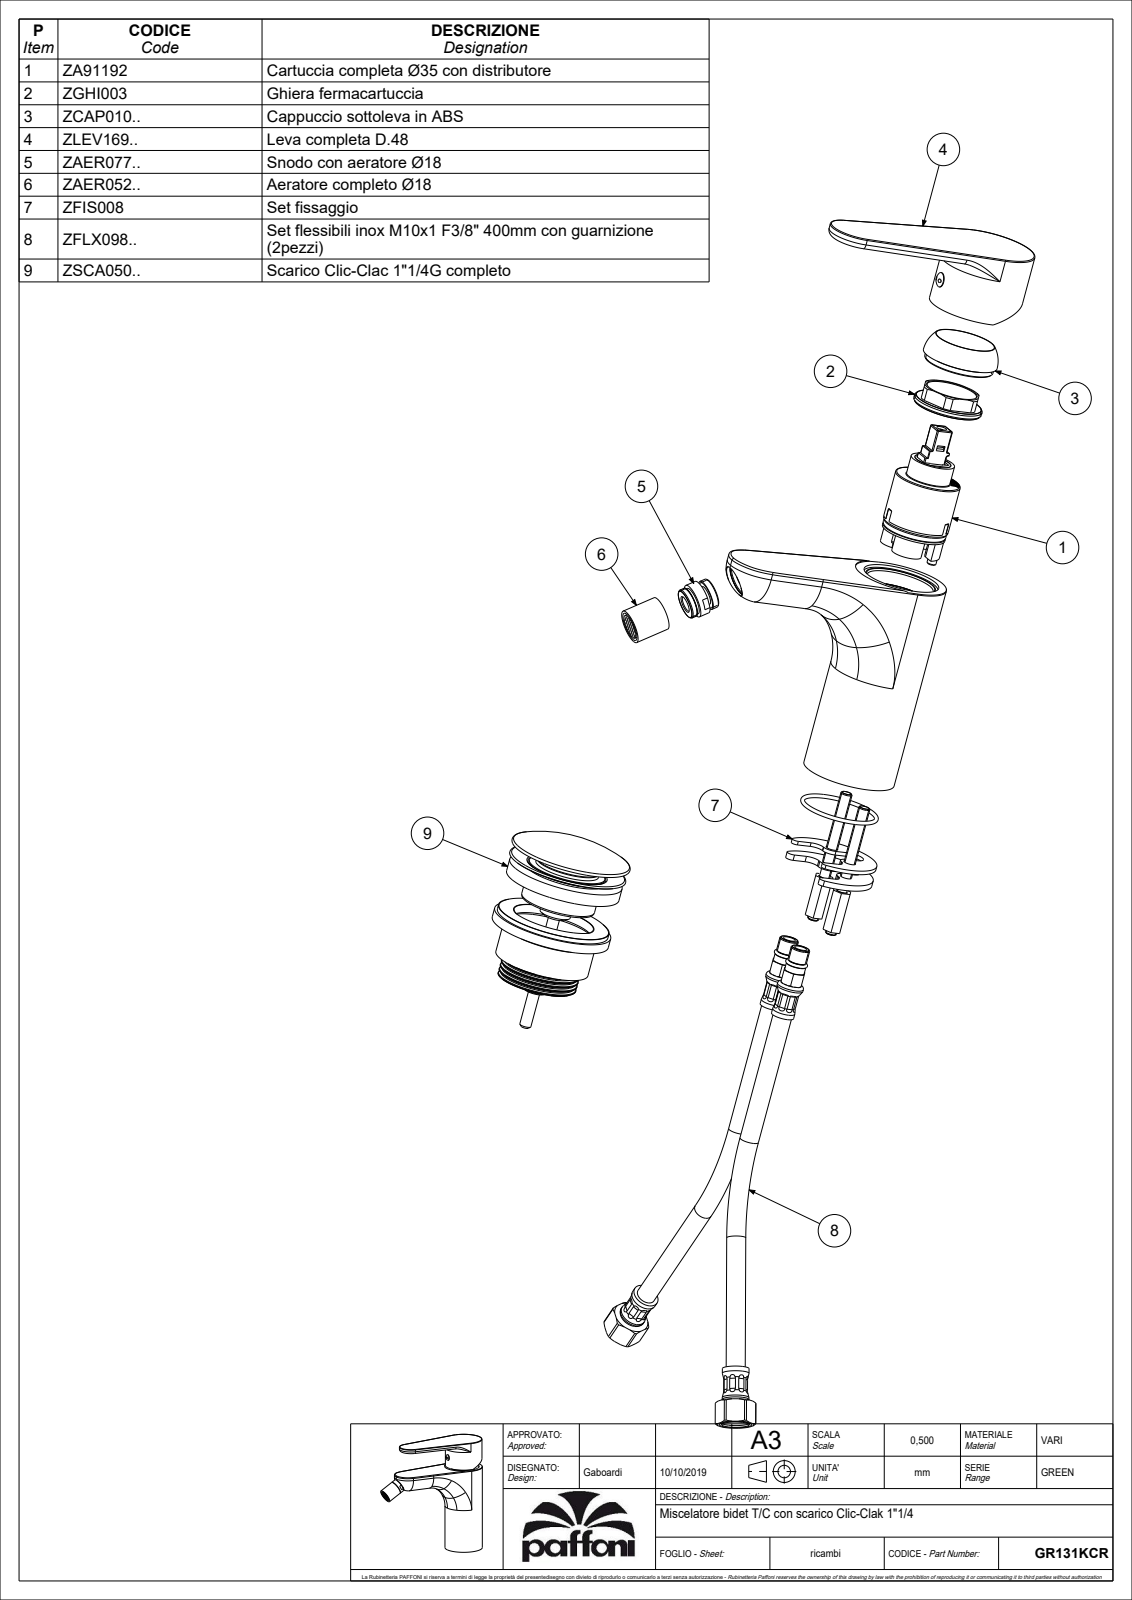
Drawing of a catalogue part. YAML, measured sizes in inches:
part_name: "GR131CR"
step_written_by: "CREO PARAMETRIC BY PTC INC, 2020044 (CONFIG_CONTROL_DESIGN)"
units: inches
bodies: {solids: 1, faces: 363, planar: 90, cylindrical: 124, other: 149}
overall_size: [5.817, 5.807, 1.929]
volume: 8.474
surface_area: 123.6
round_holes:
  - {diameter: 0.197, count: 2}
  - {diameter: 0.118, count: 1}
  - {diameter: 0.138, count: 1}
  - {diameter: 0.165, count: 1}
  - {diameter: 0.315, count: 1}
  - {diameter: 0.394, count: 1}
  - {diameter: 0.512, count: 1}
  - {diameter: 0.657, count: 1}
  - {diameter: 1.24, count: 1}
  - {diameter: 1.299, count: 1}
  - {diameter: 1.339, count: 1}
  - {diameter: 1.406, count: 1}
round_bosses_or_shafts:
  - {diameter: 1.929, count: 1}
  - {diameter: 1.89, count: 1}
  - {diameter: 1.516, count: 1}
  - {diameter: 0.709, count: 1}
  - {diameter: 0.571, count: 1}
  - {diameter: 0.354, count: 1}
  - {diameter: 0.299, count: 1}
  - {diameter: 0.217, count: 1}
partial_cylinders:
  - {radius: 0.039, count: 35}
  - {radius: 0.02, count: 8}
  - {radius: 0.118, count: 2}
  - {radius: 0.197, count: 2}
  - {radius: 0.591, count: 1}
  - {radius: 0.728, count: 1}
  - {radius: 0.984, count: 1}
face_to_face_distances: [0.118, 1.457, 1.575, 0.236, 1.22, 1.496, 1.339, 1.378, 0.079, 0.157]
hole_center_spacings: [0.484, 0.534, 0.535, 0.53, 0.531, 0.866]
